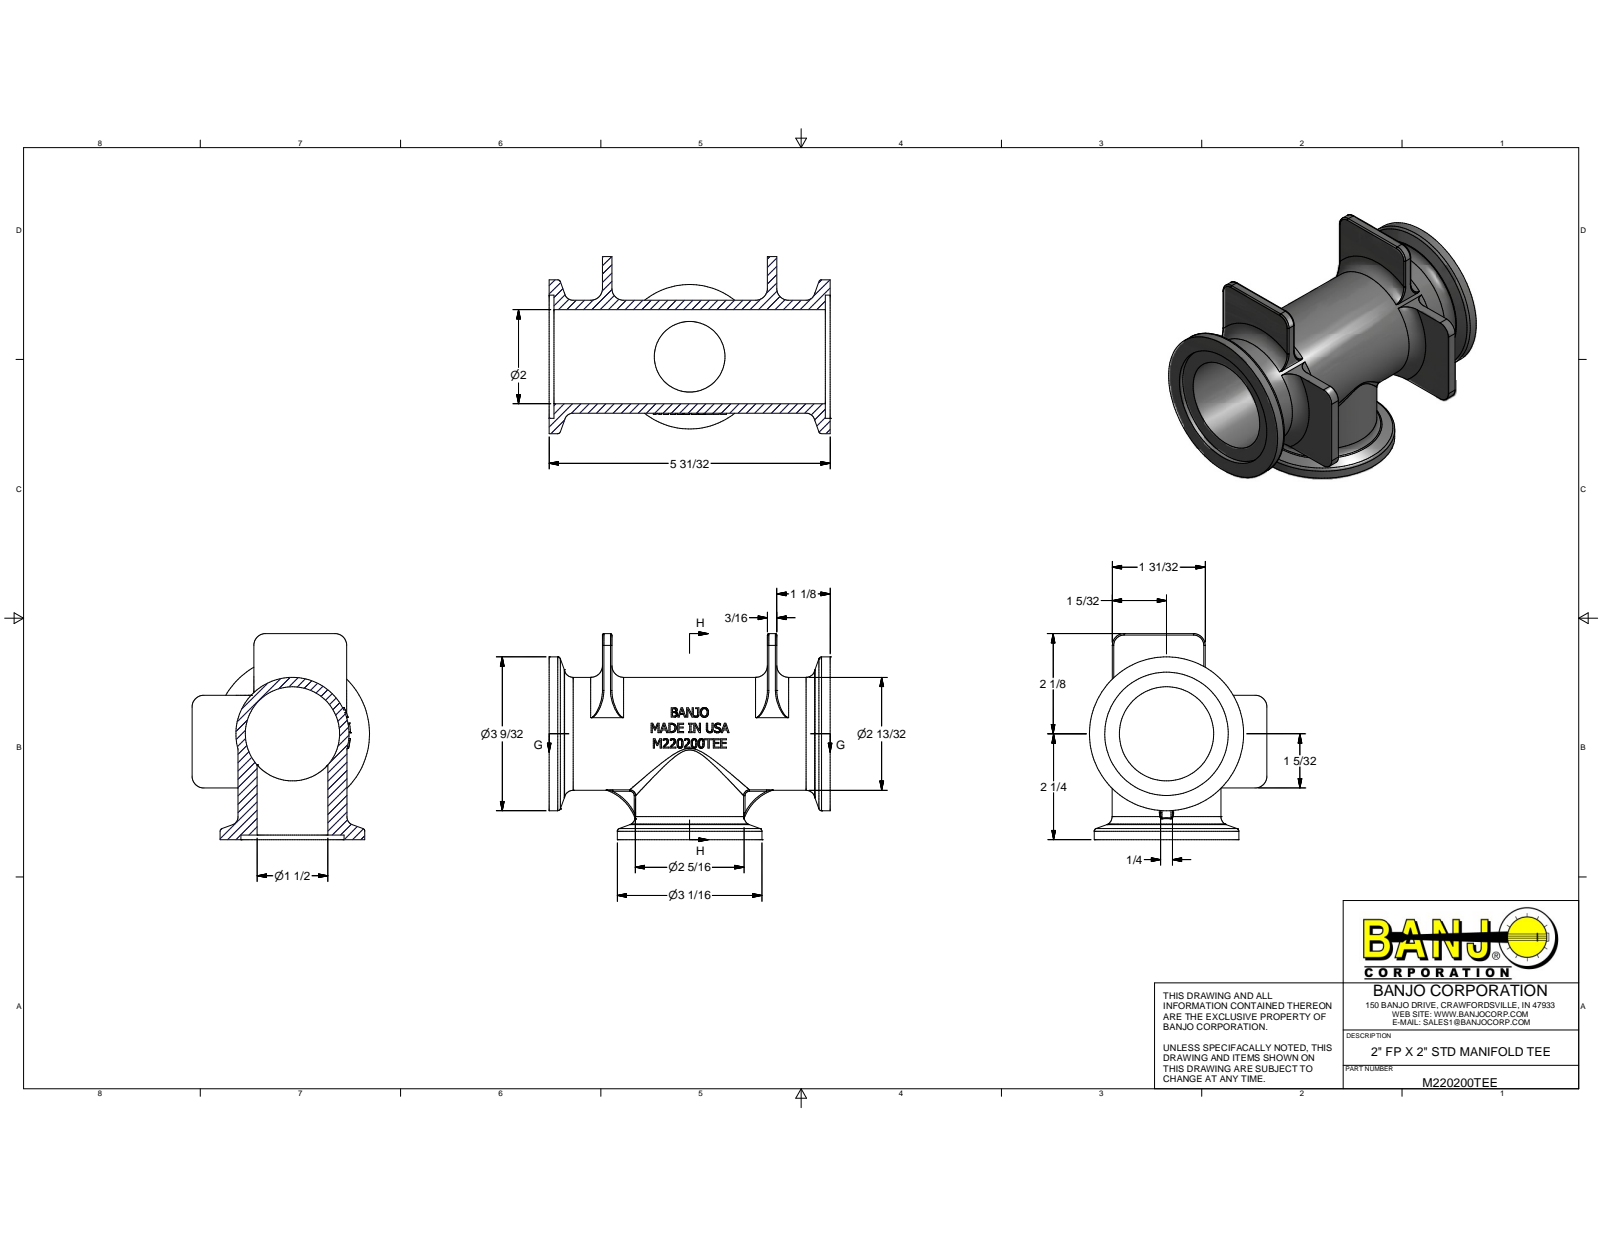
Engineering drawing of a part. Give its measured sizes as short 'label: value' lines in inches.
name: M220200TEE
written by: Autodesk Inventor 2013 (AUTOMOTIVE_DESIGN)
unit: in
bodies: 1 solid, 488 faces (216 planar, 75 cylindrical, 197 other)
size: 5.96 × 4.38 × 3.765
volume: 15.66 in³; area: 136.1 in²
holes: 1× ⌀1.5, 1× ⌀2, 1× ⌀2.19, 1× ⌀2.62
bosses: 1× ⌀3.27, 1× ⌀3.07, 1× ⌀2.4, 1× ⌀2.31
rounds: 18× R0.03, 4× R0.25, 2× R1, 1× R1.23
face distances: 0.1, 0.2, 3.5, 1.13, 1.33, 4.63, 4.83, 1.23, 5.86, 1.03
